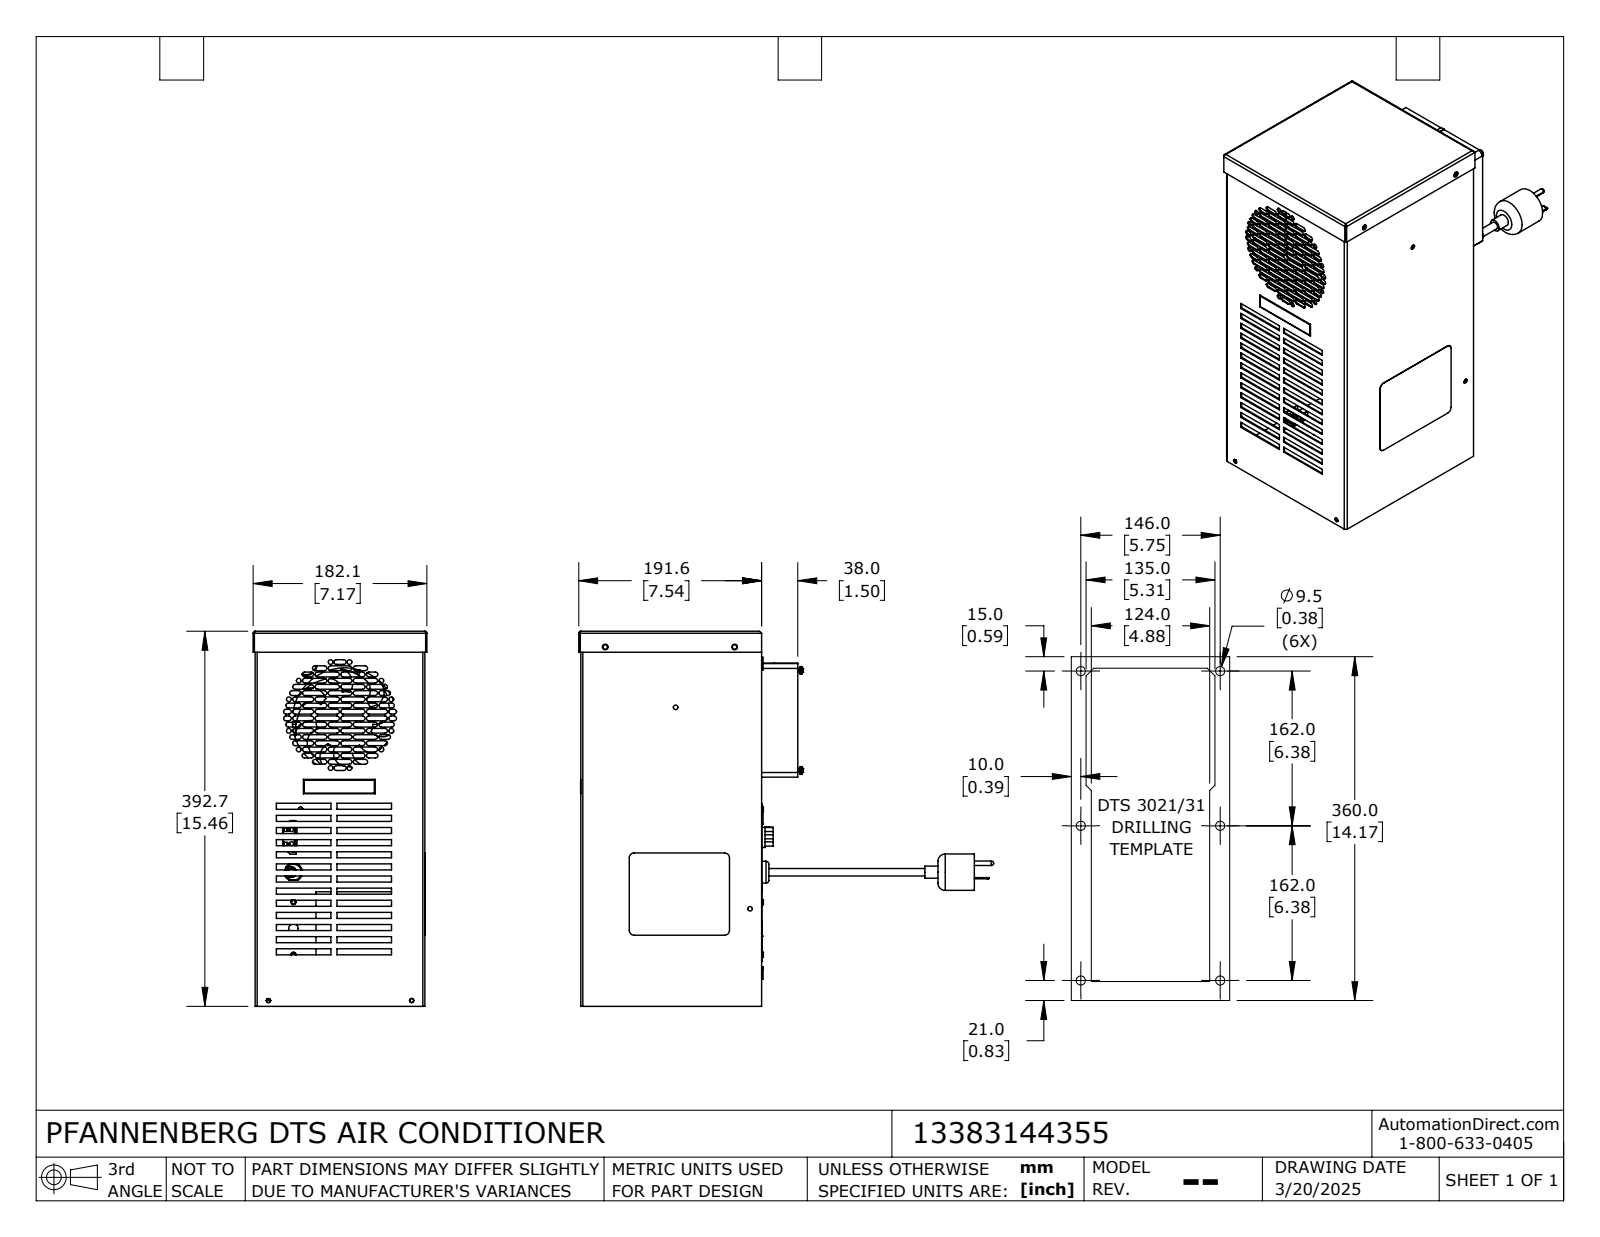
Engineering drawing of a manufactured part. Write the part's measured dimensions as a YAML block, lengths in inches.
part_name: "13383144355_Default"
step_written_by: "SolidWorks 2024 (CONFIG_CONTROL_DESIGN)"
units: inches
bodies: {solids: 27, faces: 2834, planar: 1494, cylindrical: 695, other: 645}
overall_size: [17.116, 15.461, 7.168]
volume: 53.71
surface_area: 1434
round_holes:
  - {diameter: 0.197, count: 17}
  - {diameter: 0.165, count: 9}
  - {diameter: 0.177, count: 9}
  - {diameter: 0.283, count: 6}
  - {diameter: 0.189, count: 5}
  - {diameter: 0.194, count: 5}
  - {diameter: 0.091, count: 3}
  - {diameter: 0.142, count: 3}
  - {diameter: 0.157, count: 3}
  - {diameter: 0.169, count: 3}
  - {diameter: 0.067, count: 2}
  - {diameter: 0.125, count: 2}
round_bosses_or_shafts:
  - {diameter: 0.512, count: 6}
  - {diameter: 0.315, count: 4}
  - {diameter: 0.272, count: 3}
  - {diameter: 0.157, count: 3}
  - {diameter: 0.5, count: 2}
  - {diameter: 2.362, count: 1}
  - {diameter: 1.5, count: 1}
  - {diameter: 0.9, count: 1}
partial_cylinders:
  - {radius: 0.098, count: 140}
  - {radius: 0.02, count: 12}
  - {radius: 0.036, count: 8}
  - {radius: 0.084, count: 8}
  - {radius: 0.039, count: 7}
  - {radius: 0.547, count: 7}
  - {radius: 0.597, count: 7}
  - {radius: 2.224, count: 7}
face_to_face_distances: [0.048, 6.952, 7.41, 0.083, 6.87, 7, 6.905, 7.362, 7.457, 6.917]
hole_center_spacings: [0.291, 2.917, 4.126, 8.586, 2.227, 5.748, 6.378, 0.295]
